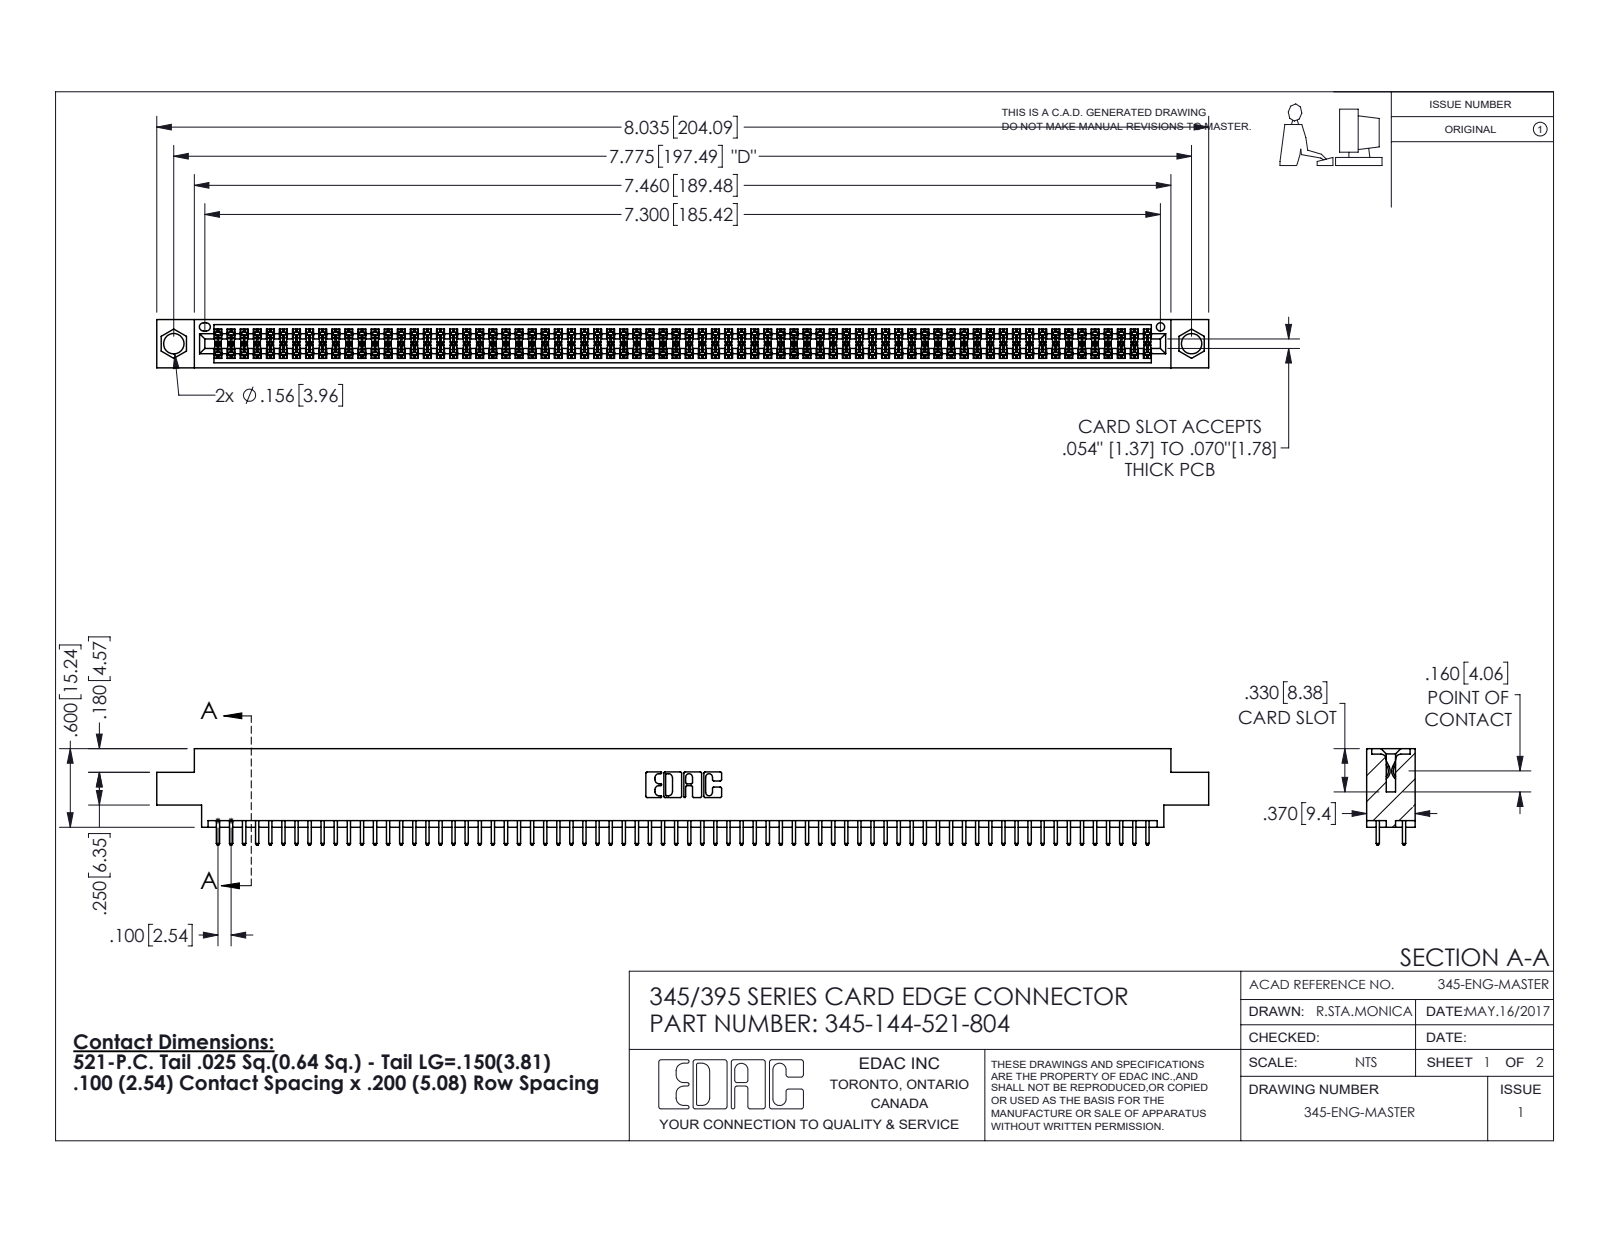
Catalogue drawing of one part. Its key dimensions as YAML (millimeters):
part_name: "345-292-001_345-293-121; 345-144-521-804; 345 Part_0.170 Offset - 0.156 Dia-TI"
step_written_by: "SolidWorks 2020 (CONFIG_CONTROL_DESIGN)"
units: millimeters
bodies: {solids: 145, faces: 7344, planar: 4850, cylindrical: 2494, other: 0}
overall_size: [204.1, 18.7, 9.4]
volume: 19830
surface_area: 29500
round_holes:
  - {diameter: 4, count: 2}
  - {diameter: 1.6, count: 1}
partial_cylinders:
  - {radius: 0.2, count: 288}
  - {radius: 0.3, count: 144}
  - {radius: 0.3, count: 22}
  - {radius: 0.2, count: 6}
  - {radius: 0.8, count: 6}
  - {radius: 0.7, count: 3}
  - {radius: 0.4, count: 2}
  - {radius: 0.5, count: 2}
face_to_face_distances: [1.8, 7.6, 5.1, 9.4, 2.5, 6.9, 0.6, 5.7, 4.4, 3.8]
hole_center_spacings: [6.9, 191.5, 197.5]
